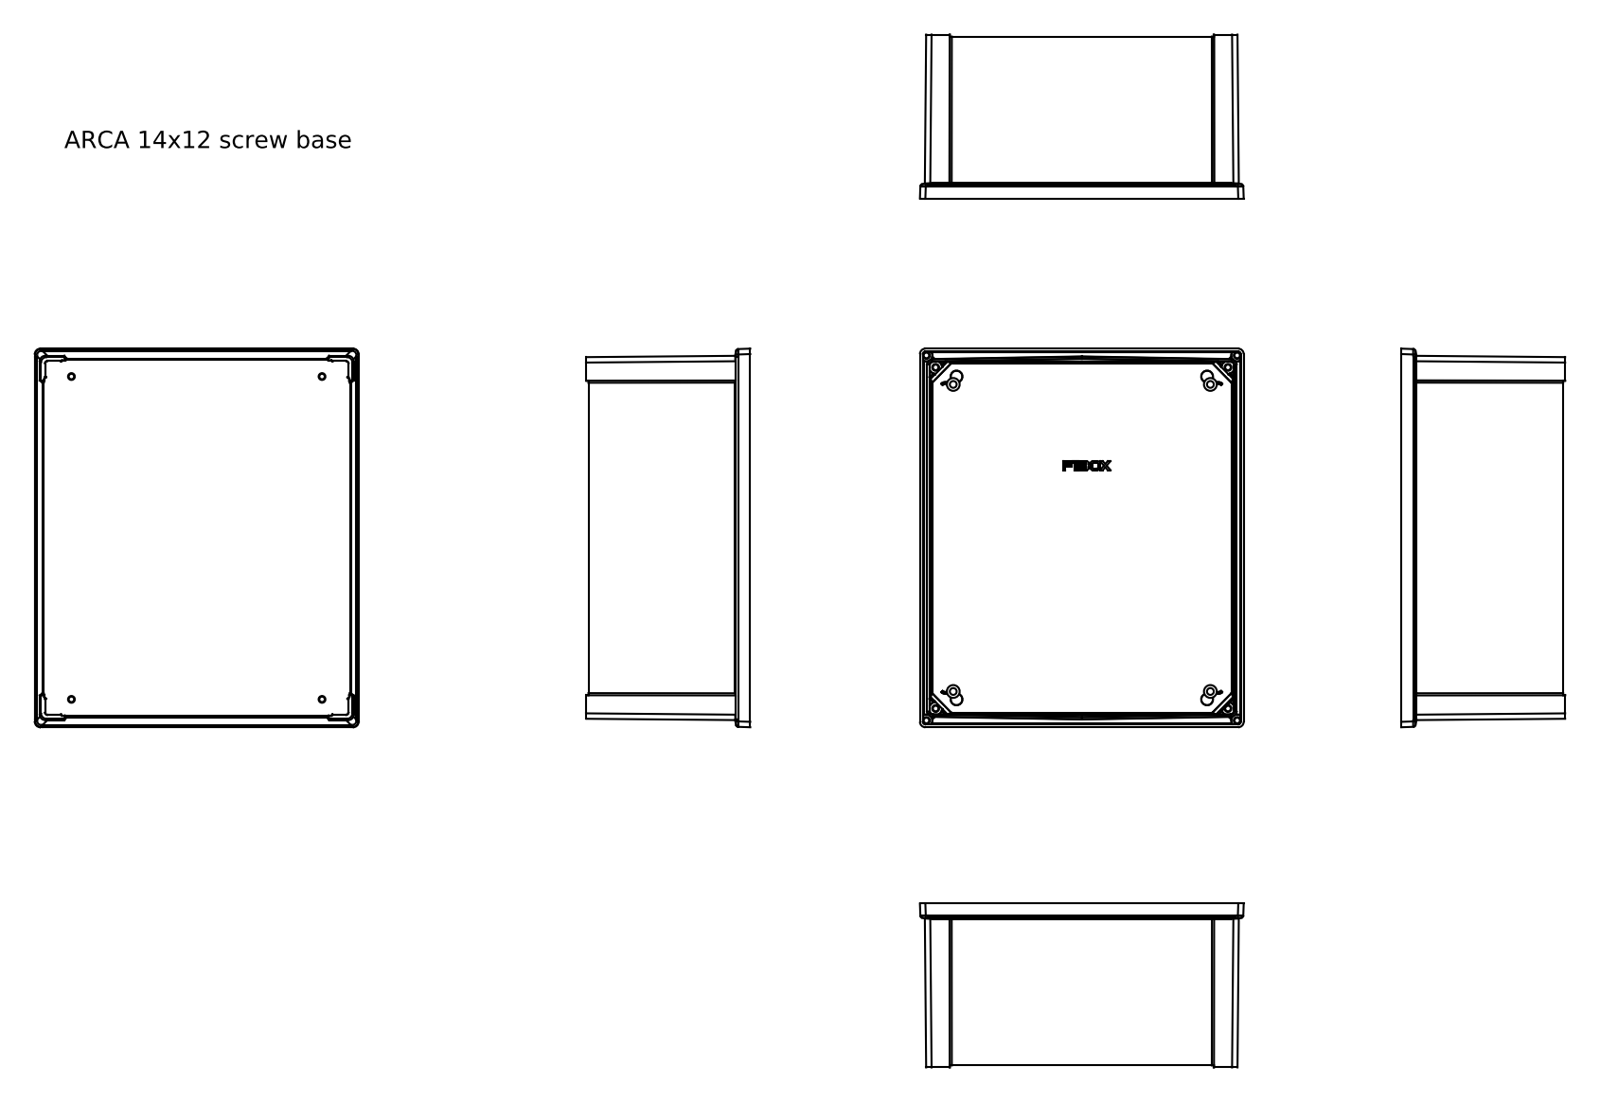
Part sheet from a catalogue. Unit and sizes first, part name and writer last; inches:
Units: inches
Overall size (bounding box): 15.108 × 12.919 × 6.535
Round holes (diameter × count): ⌀0.272 ×4
Round bosses / shafts (diameter × count): ⌀0.512 ×4
Partial cylindrical surfaces — rounded edges, fillets, slot ends (radius × count): R0.098 ×16, R0.217 ×12, R0.101 ×6, R0.02 ×4, R0.038 ×4, R0.138 ×4, R0.886 ×4, R1.043 ×4
Main face-to-face distances: 0.142, 0.118, 0.104, 0.104, 0.367, 0.249, 0.157, 12.609, 12.491, 12.242
Hole centre spacings: 10.26, 12.252, 15.98
Volume: 83.66 in³ · Surface area: 1 093 in²
Bodies: 6 solids, 484 faces (285 planar, 72 cylindrical, 127 other)
Part name (STEP PRODUCT): 14x12_screw_base
STEP written by: SolidWorks 2015 (AUTOMOTIVE_DESIGN)
